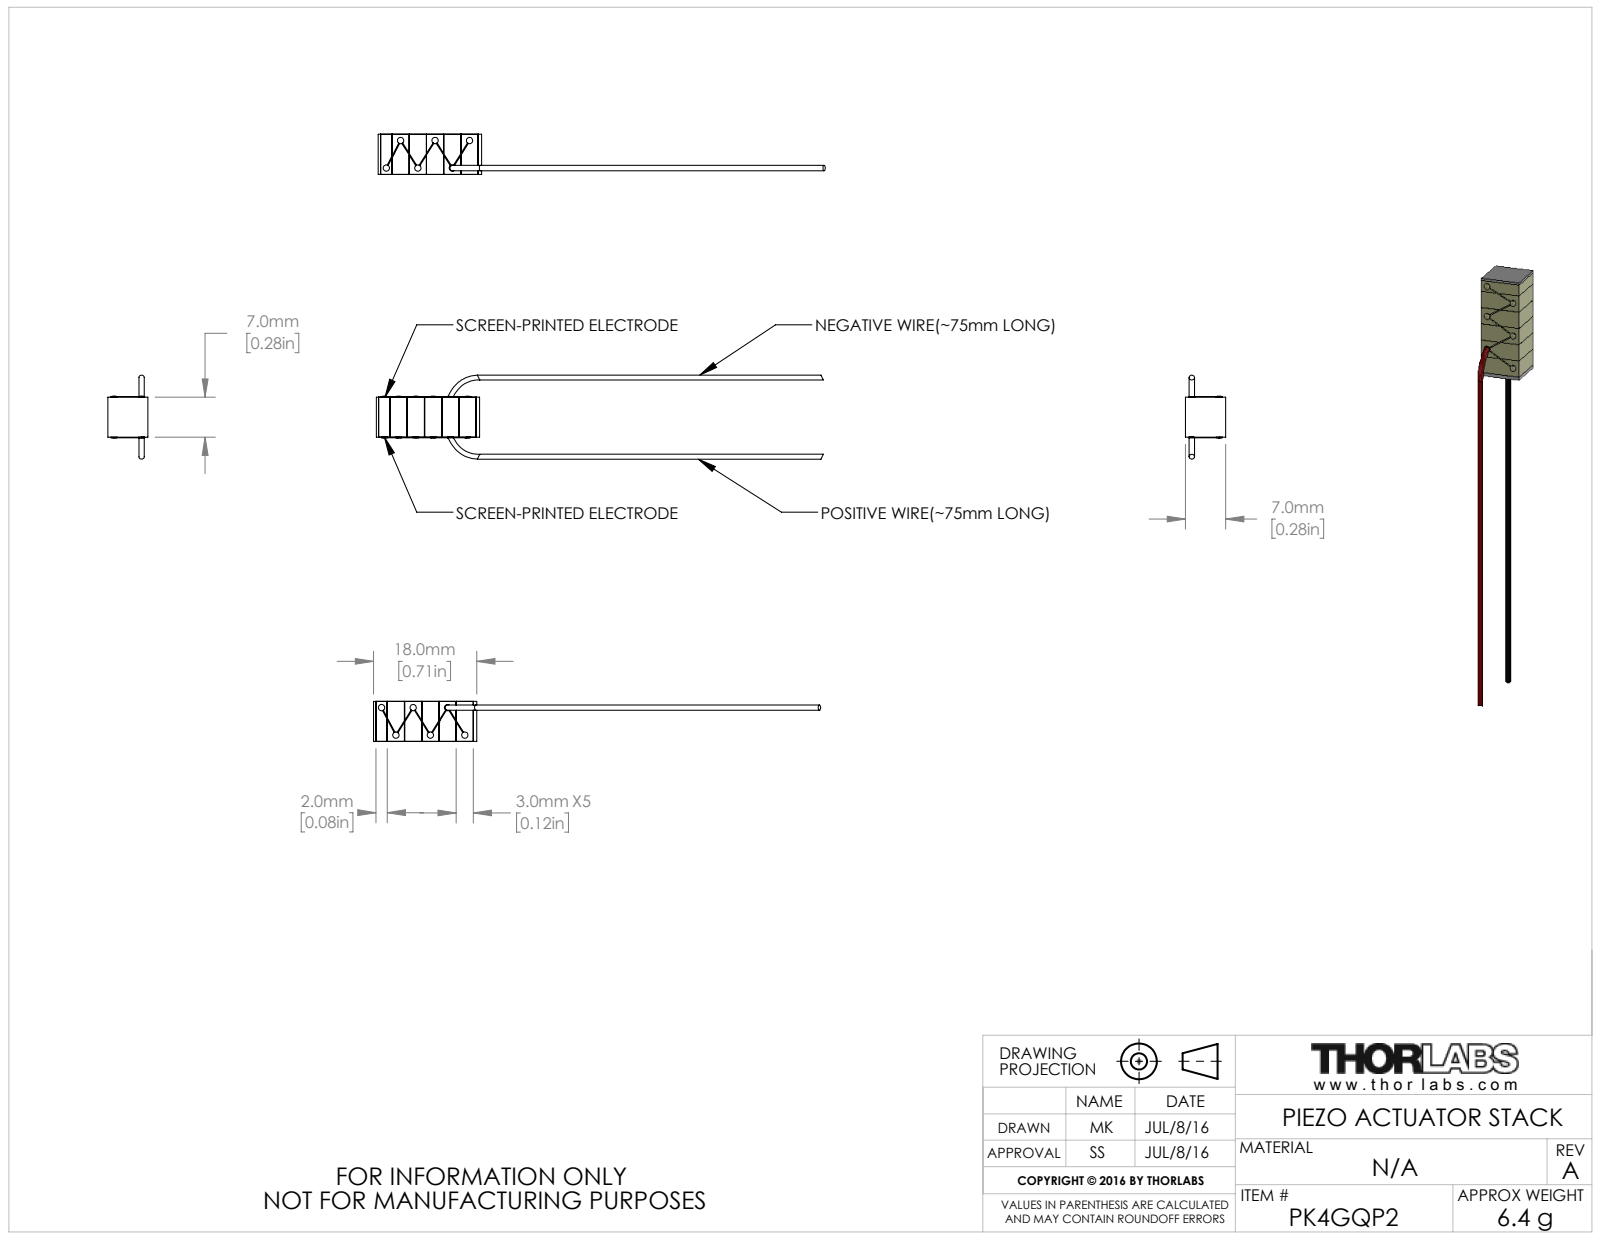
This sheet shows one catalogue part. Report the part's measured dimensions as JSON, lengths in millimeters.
{"part_name": "CTN003158", "step_written_by": "SolidWorks 2016 (AUTOMOTIVE_DESIGN)", "units": "millimeters", "bodies": {"solids": 4, "faces": 216, "planar": 122, "cylindrical": 36, "other": 58}, "overall_size": [78.05, 14.66, 7], "volume_mm3": 1800, "surface_area_mm2": 2752, "round_bosses_or_shafts": [[1.1, 6]], "face_to_face_distances": [3.01, 3, 7, 6.01, 6.02, 9.02, 12.03, 9.03, 3.02, 15.03]}
